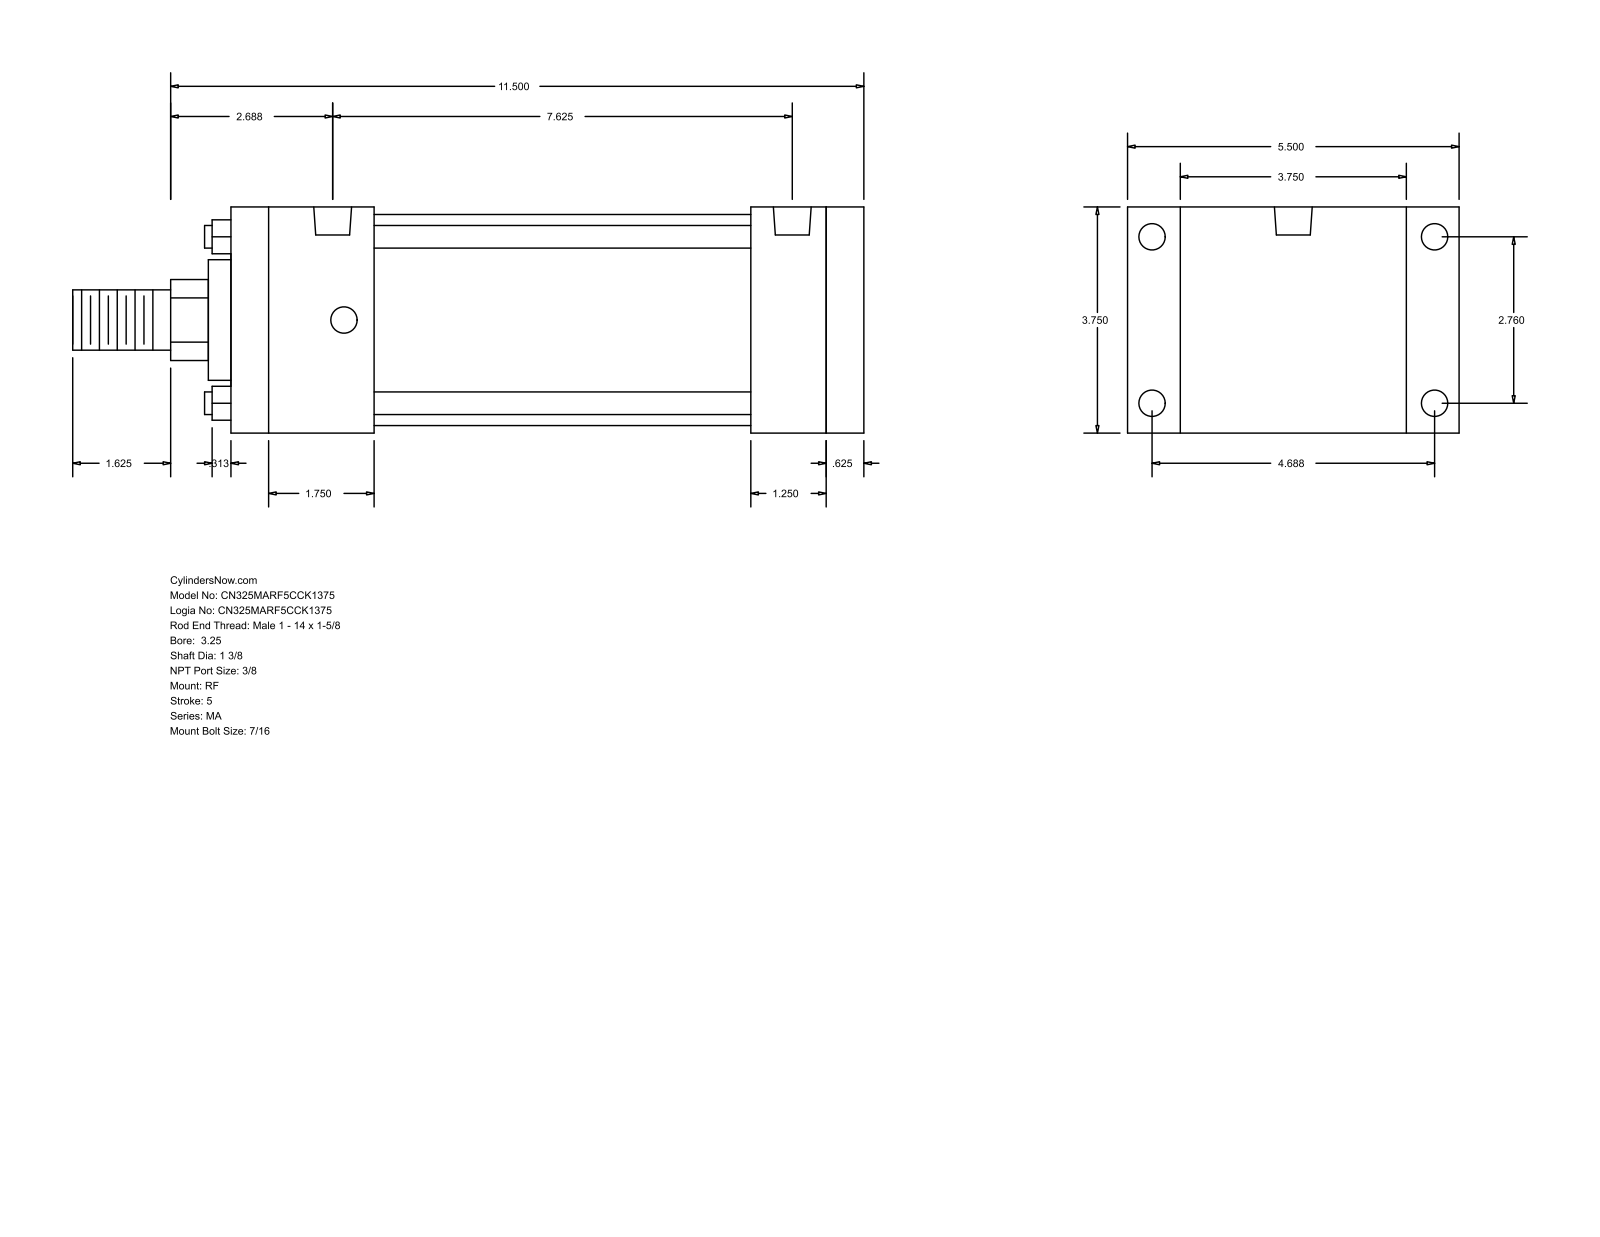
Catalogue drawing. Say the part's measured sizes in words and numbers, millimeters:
The part is named "MA_RF__0325_1.375". Its 3-D file was written by "GSSL Pune (CONFIG_CONTROL_DESIGN)". It is 0 solids with 92 faces: 64 planar, 28 cylindrical and 0 other. Overall it measures 333.38 by 139.7 by 95.25 millimeters. Round holes: 8 of diameter 11.11, 2 of diameter 15.93. Round bosses or shafts: 4 of diameter 9.53, 1 of diameter 88.9, 1 of diameter 50.8, 1 of diameter 34.92, 1 of diameter 25.4. Partial cylindrical surfaces (rounded edges, fillets, slot ends): 1 of radius 17.06. The main face-to-face distances are 95.24, 266.7, 250.83, 15.87, 22.23, 117.47, 219.07, 31.76, 47.63, 60.32. The hole center spacings are 70.1, 119.06, 138.16, 184.15, 4.76, 4.77, 188.91, 188.92.
